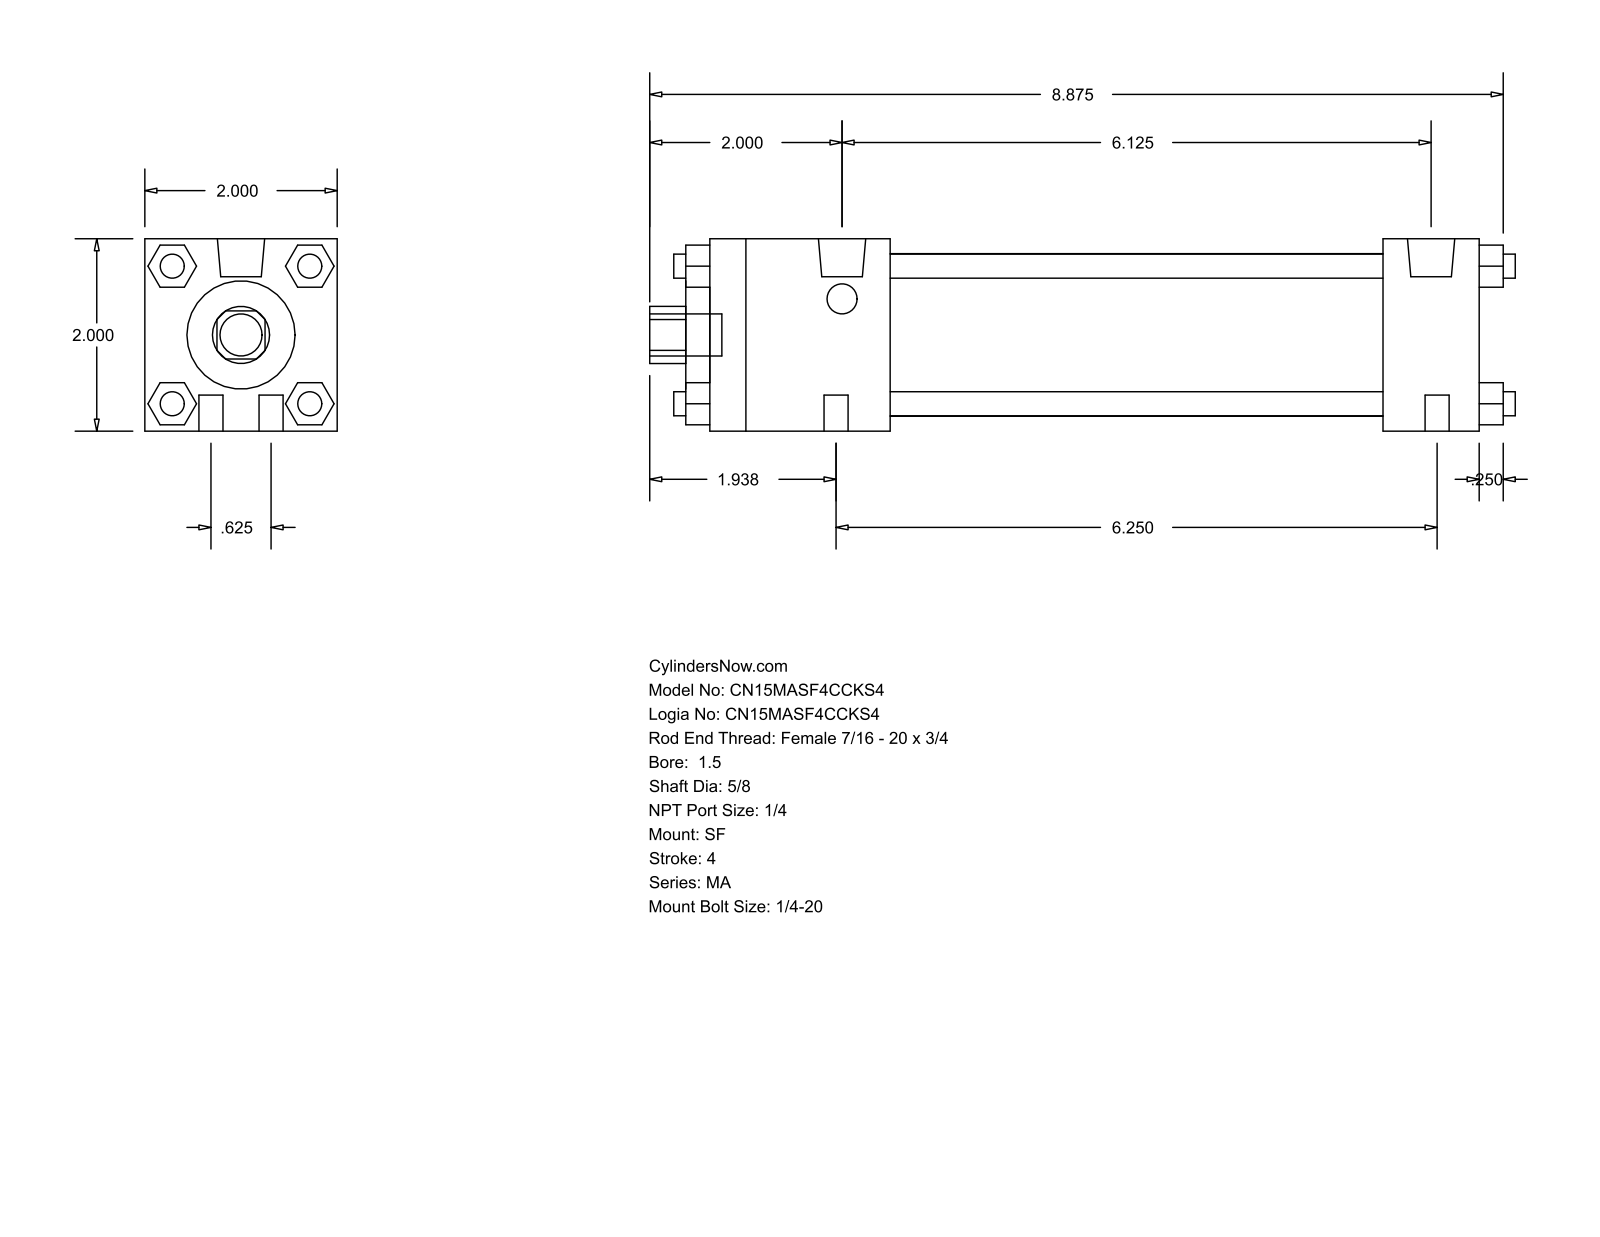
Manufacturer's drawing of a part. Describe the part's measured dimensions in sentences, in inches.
The part is named "MA_SF__0150_0.625". Its 3-D file was written by "GSSL Pune (CONFIG_CONTROL_DESIGN)". It is 0 solids with 124 faces: 94 planar, 30 cylindrical and 0 other. Overall it measures 9 by 2 by 2 inches. Round holes: 1 of diameter 0.625, 1 of diameter 1.125, 1 of diameter 1.69. Round bosses or shafts: 8 of diameter 0.25, 2 of diameter 0.492, 2 of diameter 0.313, 1 of diameter 0.437. Partial cylindrical surfaces (rounded edges, fillets, slot ends): 1 of radius 0.297. The main face-to-face distances are 2, 8, 1.875, 7, 5.125, 6.125, 1, 0.25, 2.125, 7.25.
